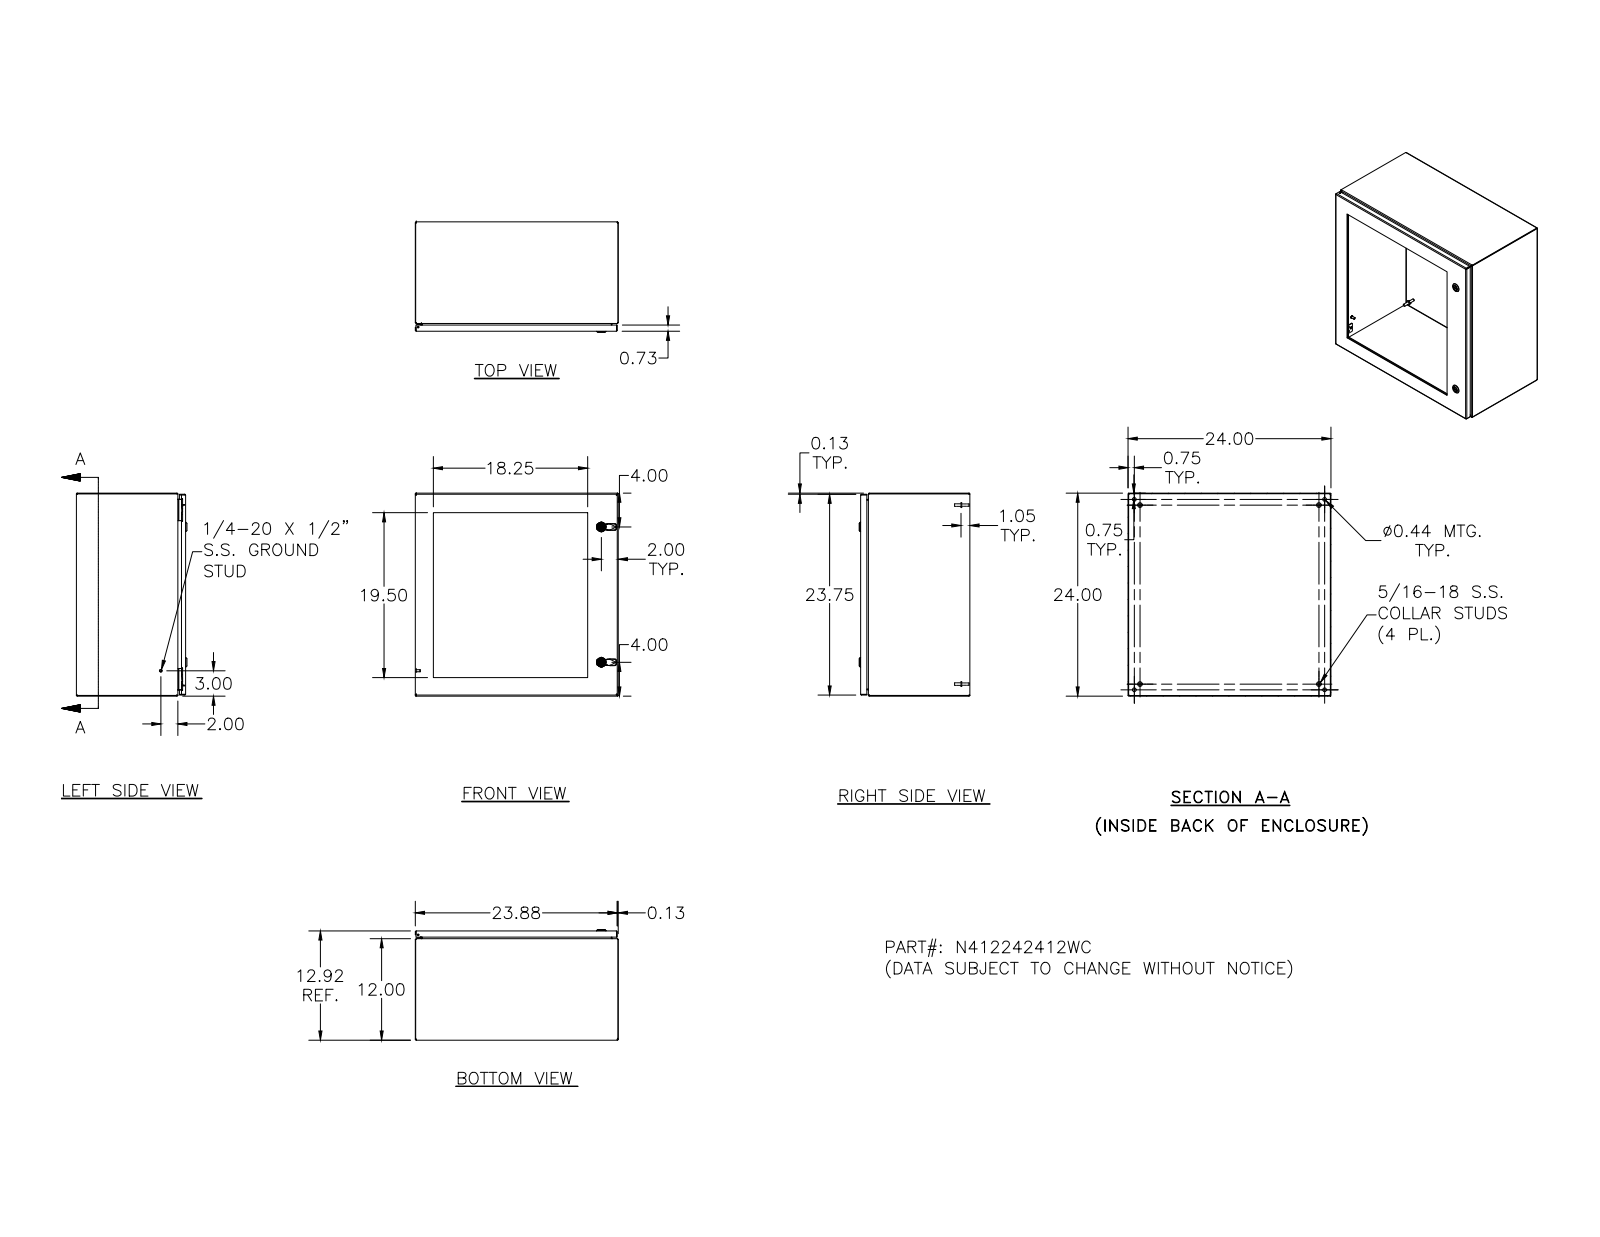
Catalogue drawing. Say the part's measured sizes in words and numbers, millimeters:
The part is named "N412242412WC". Its 3-D file was written by "SolidWorks 2018 (AUTOMOTIVE_DESIGN)". It is 84 solids with 2510 faces: 971 planar, 762 cylindrical and 777 other. Overall it measures 609.6 by 609.6 by 332.1 millimeters. Its volume is 4 331 000 cubic millimeters and its surface area 3 436 000 square millimeters. Round holes: 22 of diameter 4, 20 of diameter 7.1, 5 of diameter 4.8, 4 of diameter 2.4, 4 of diameter 3.9, 4 of diameter 4.2, 4 of diameter 4.4, 4 of diameter 11.1, 2 of diameter 5, 2 of diameter 8, 2 of diameter 10, 2 of diameter 10.2. Round bosses or shafts: 20 of diameter 8.6, 20 of diameter 4.8, 10 of diameter 6.4, 4 of diameter 14.3, 4 of diameter 9.1, 4 of diameter 8.1, 4 of diameter 7.6, 4 of diameter 7. Partial cylindrical surfaces (rounded edges, fillets, slot ends): 54 of radius 0.3, 34 of radius 0.8, 26 of radius 1.3, 24 of radius 2.7, 23 of radius 0.5, 18 of radius 0.4, 16 of radius 3.2, 8 of radius 0.8. The main face-to-face distances are 1.9, 607.7, 326.2, 324.3, 605.8, 609.6, 6.4, 319.9, 318, 328.1. The hole center spacings are 101.6, 203.2, 536.8, 304.8, 508, 564.9, 527.1, 158.
